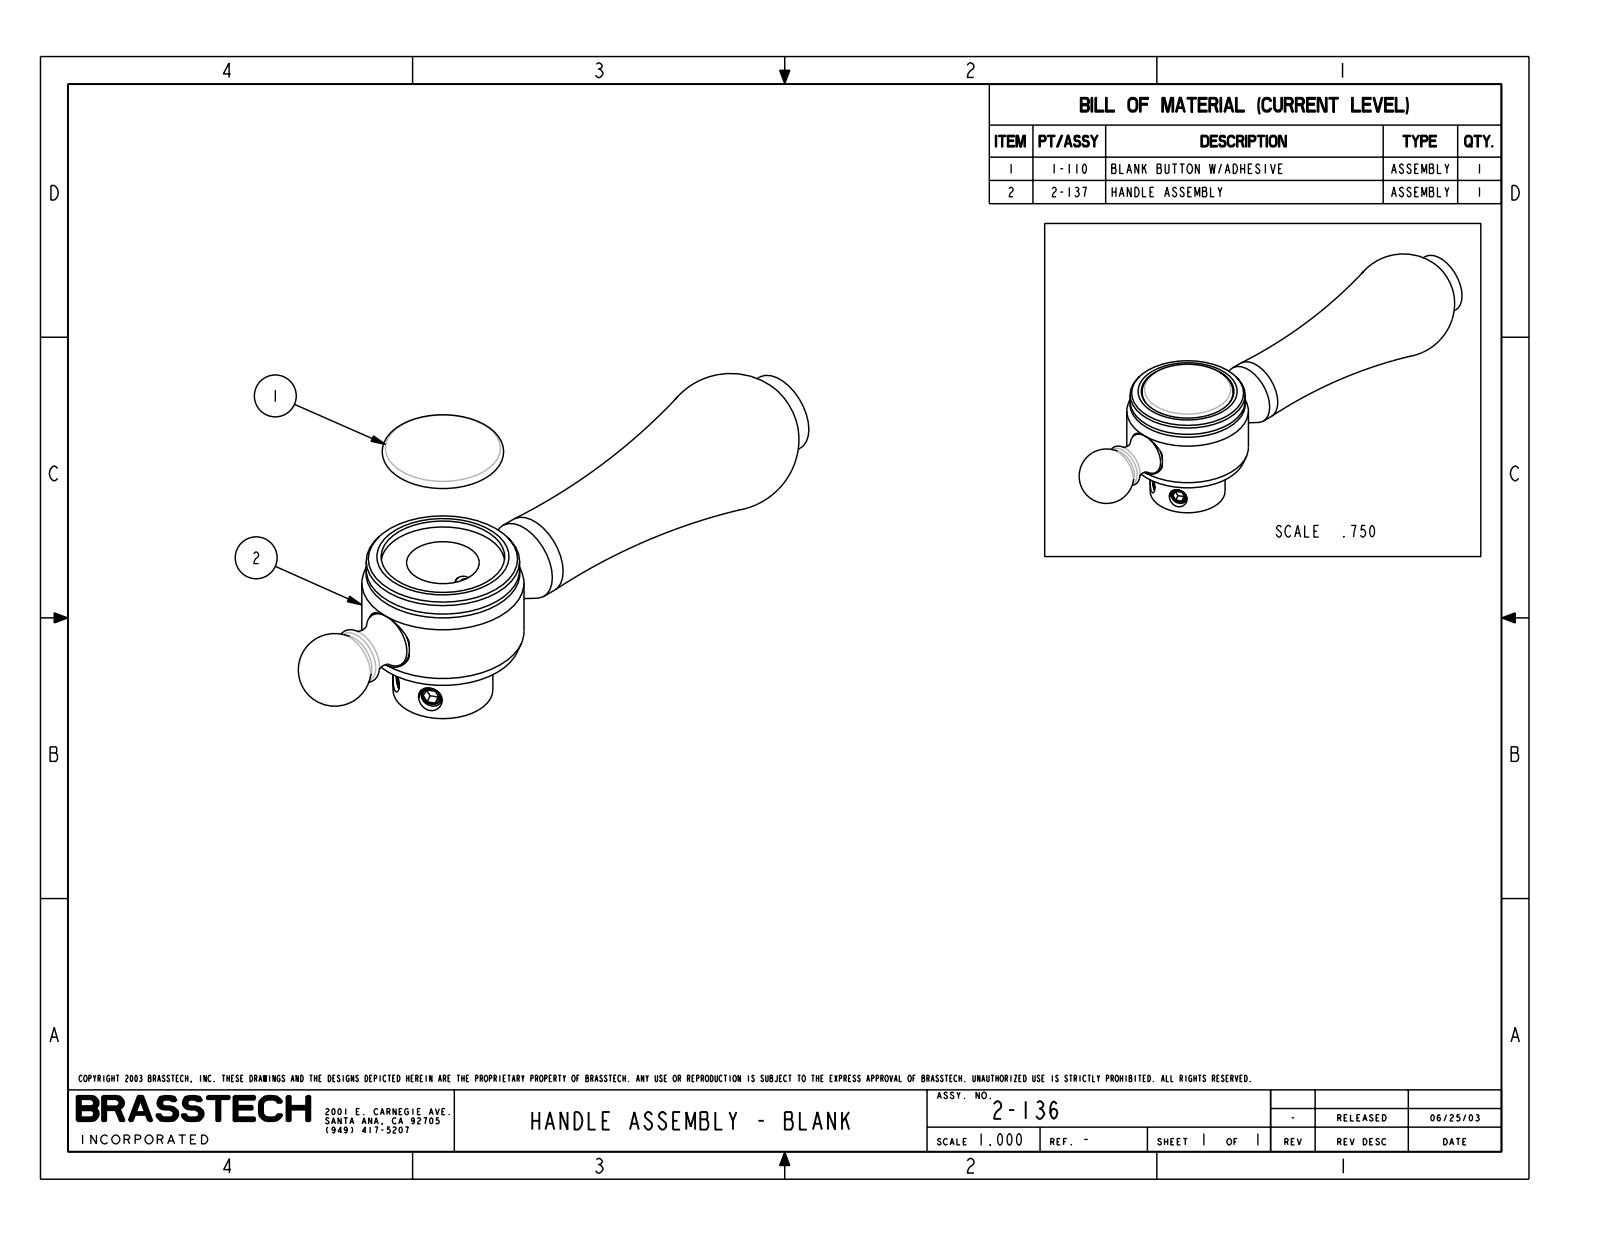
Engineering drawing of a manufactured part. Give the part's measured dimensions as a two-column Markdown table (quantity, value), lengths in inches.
| quantity | value |
| --- | --- |
| part name | 2-136_SW0001 |
| STEP written by | PRO/ENGINEER BY PARAMETRIC TECHNOLOGY CORPORATION, 2009300 (CONFIG_CONTROL_DESIGN) |
| units | inches |
| bodies | 0 solids, 62 faces (5 planar, 17 cylindrical, 40 other) |
| overall size | 4.675 × 1.195 × 1.115 |
| round holes (diameter × count) | 0.41 × 1 |
| round bosses / shafts (diameter × count) | 1.115 × 1, 1.055 × 1, 0.687 × 1, 0.563 × 1, 0.394 × 1, 0.392 × 1 |
| main face-to-face distances | 0.761, 0.359, 1.12, 3.799 |
